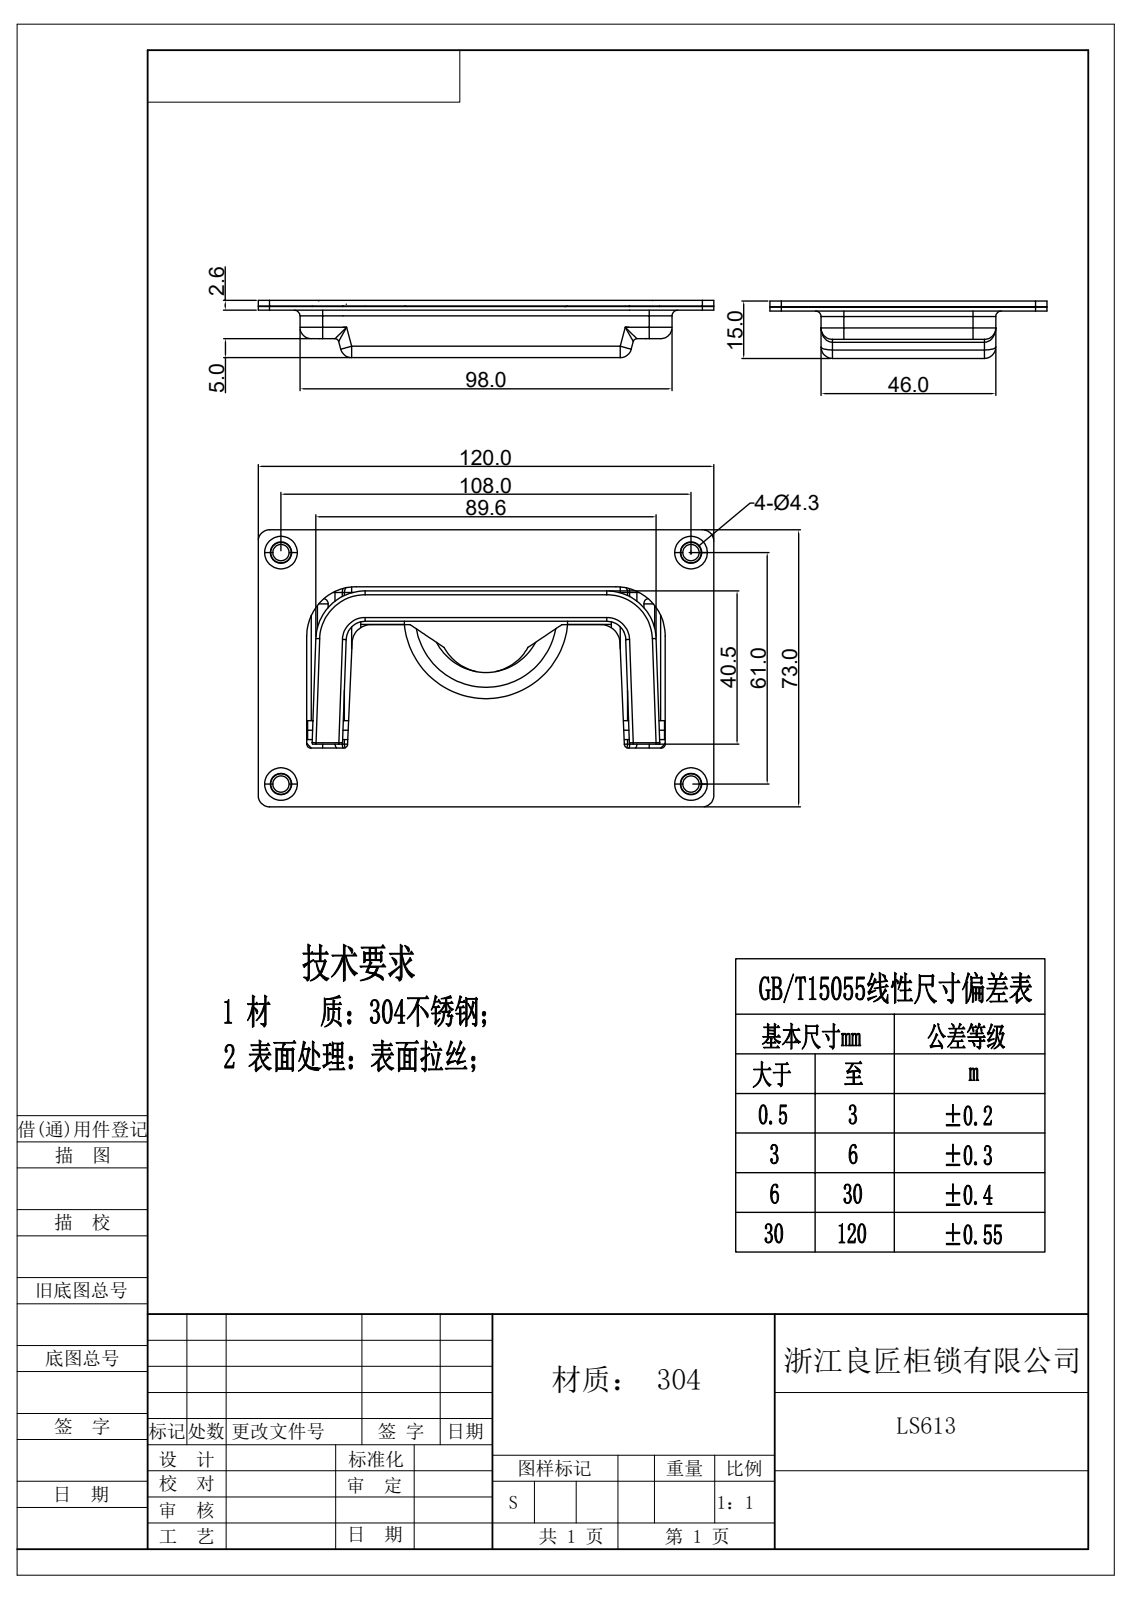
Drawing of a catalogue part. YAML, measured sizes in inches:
step_written_by: "Rhino 8.5 (CONFIG_CONTROL_DESIGN)"
units: inches
bodies: {solids: 5, faces: 312, planar: 79, cylindrical: 141, other: 92}
overall_size: [4.724, 2.874, 0.594]
volume: 2.162
surface_area: 75.99
round_holes:
  - {diameter: 0.169, count: 4}
  - {diameter: 0.205, count: 1}
  - {diameter: 0.217, count: 1}
round_bosses_or_shafts:
  - {diameter: 0.197, count: 1}
partial_cylinders:
  - {radius: 0.039, count: 27}
  - {radius: 0.118, count: 18}
  - {radius: 0.059, count: 16}
  - {radius: 0.079, count: 15}
  - {radius: 0.197, count: 8}
  - {radius: 0.02, count: 6}
  - {radius: 0.098, count: 5}
  - {radius: 0.236, count: 4}
face_to_face_distances: [0.039, 0.059, 0.492, 0.063, 0.043, 0.102, 0.531, 0.453, 0.535, 0.594]
hole_center_spacings: [2.296, 2.402, 2.622, 4.252, 4.883]
